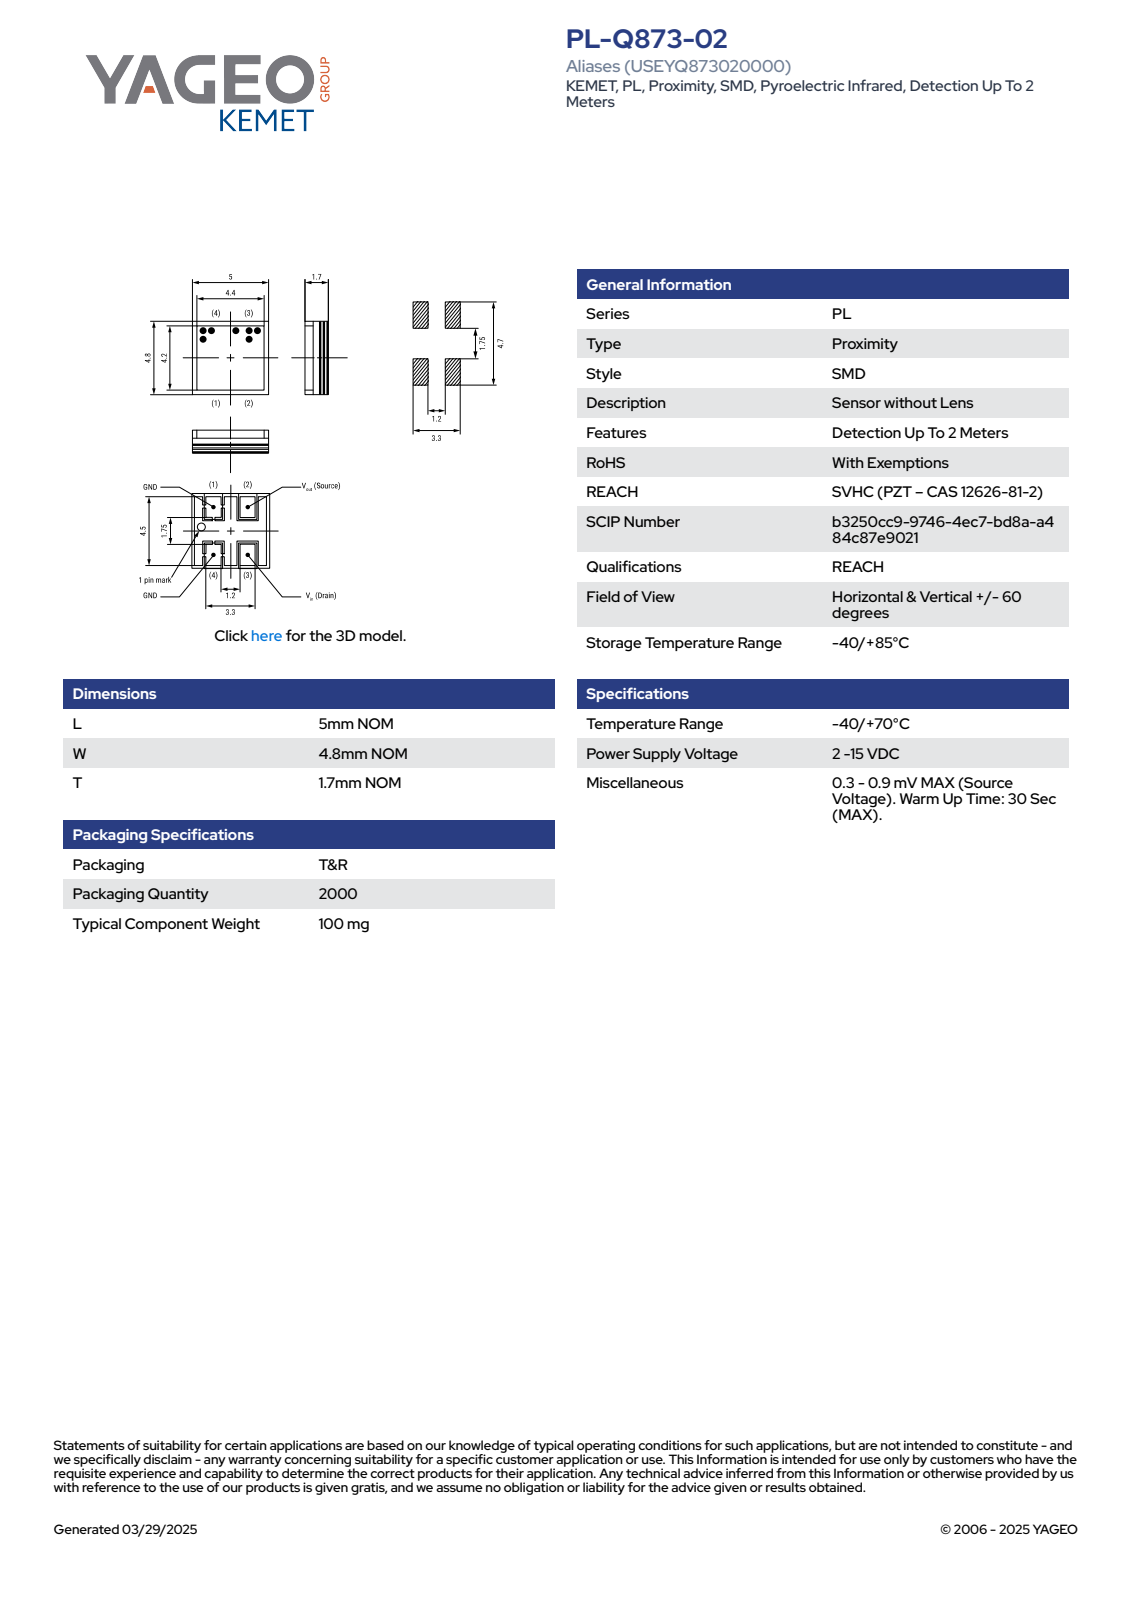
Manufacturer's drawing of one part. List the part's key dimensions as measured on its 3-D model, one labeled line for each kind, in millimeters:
Part name (STEP PRODUCT): Default
STEP written by: SolidWorks 2014 (AUTOMOTIVE_DESIGN)
Units: millimetres
Bodies: 1 solid, 89 faces (87 planar, 2 cylindrical, 0 other)
Overall size (bounding box): 5 × 4.8 × 1.7
Volume: 41 mm³ · Surface area: 81 mm²
Round holes (diameter × count): ⌀0.37 ×1
Main face-to-face distances: 1.7, 1.69, 4.8, 5, 1.68, 4.5, 4.75, 4.65, 4.35, 4.7
